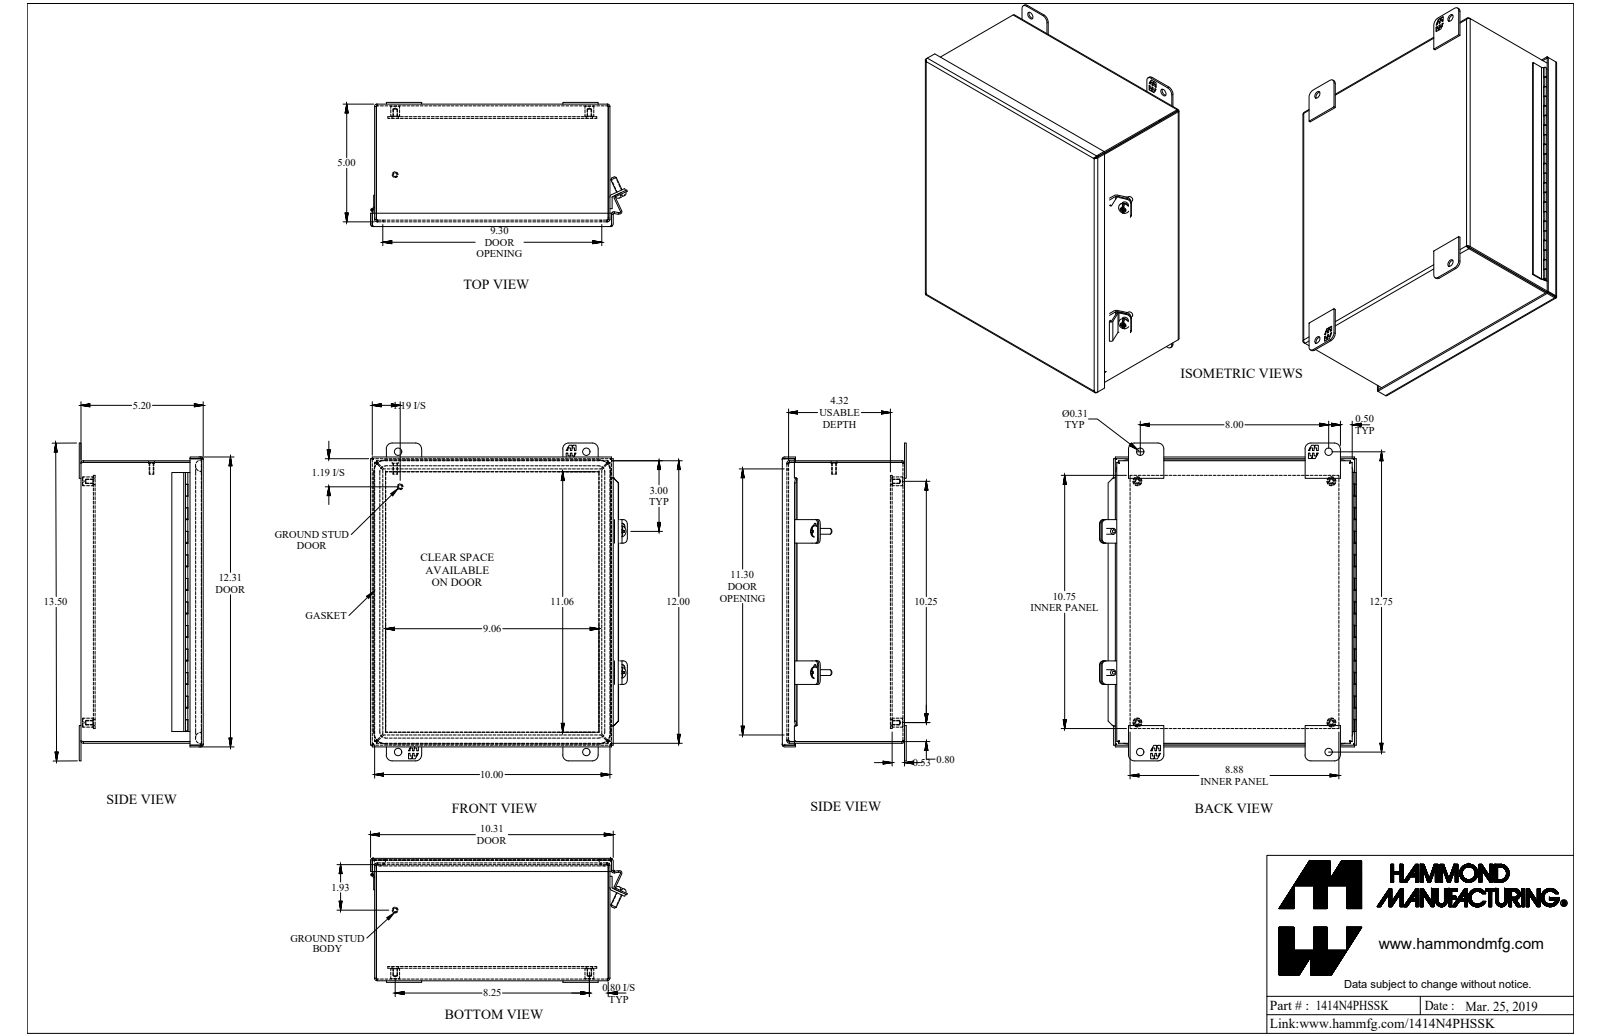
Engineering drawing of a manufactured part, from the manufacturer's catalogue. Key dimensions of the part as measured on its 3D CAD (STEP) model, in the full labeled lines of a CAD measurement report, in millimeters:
Part name (STEP PRODUCT): 1414N4PHSSK
STEP written by: SolidWorks 2018 (AUTOMOTIVE_DESIGN)
Units: millimetres
Bodies: 21 solids, 724 faces (464 planar, 196 cylindrical, 64 other)
Overall size (bounding box): 342.9 × 276.9 × 133.8
Volume: 791 200 mm³ · Surface area: 874 800 mm²
Round holes (diameter × count): ⌀4 ×4, ⌀6.7 ×4, ⌀8 ×4, ⌀5.4 ×2, ⌀1.3 ×1
Round bosses / shafts (diameter × count): ⌀9.5 ×4, ⌀6.4 ×4, ⌀12.2 ×2, ⌀4.8 ×2, ⌀2.5 ×1, ⌀1.1 ×1
Partial cylindrical surfaces — rounded edges, fillets, slot ends (radius × count): R6.4 ×24, R0.9 ×9, R2.7 ×9, R1.2 ×8, R3 ×8, R4.8 ×8, R3.6 ×4, R12.7 ×4
Main face-to-face distances: 1.8, 130.2, 116.7, 13.5, 132, 128.3, 252.2, 15.3, 118.5, 11.7
Hole centre spacings: 357.7, 208.8, 334.2, 31.9, 31.9, 209.6, 209.6, 260.4
